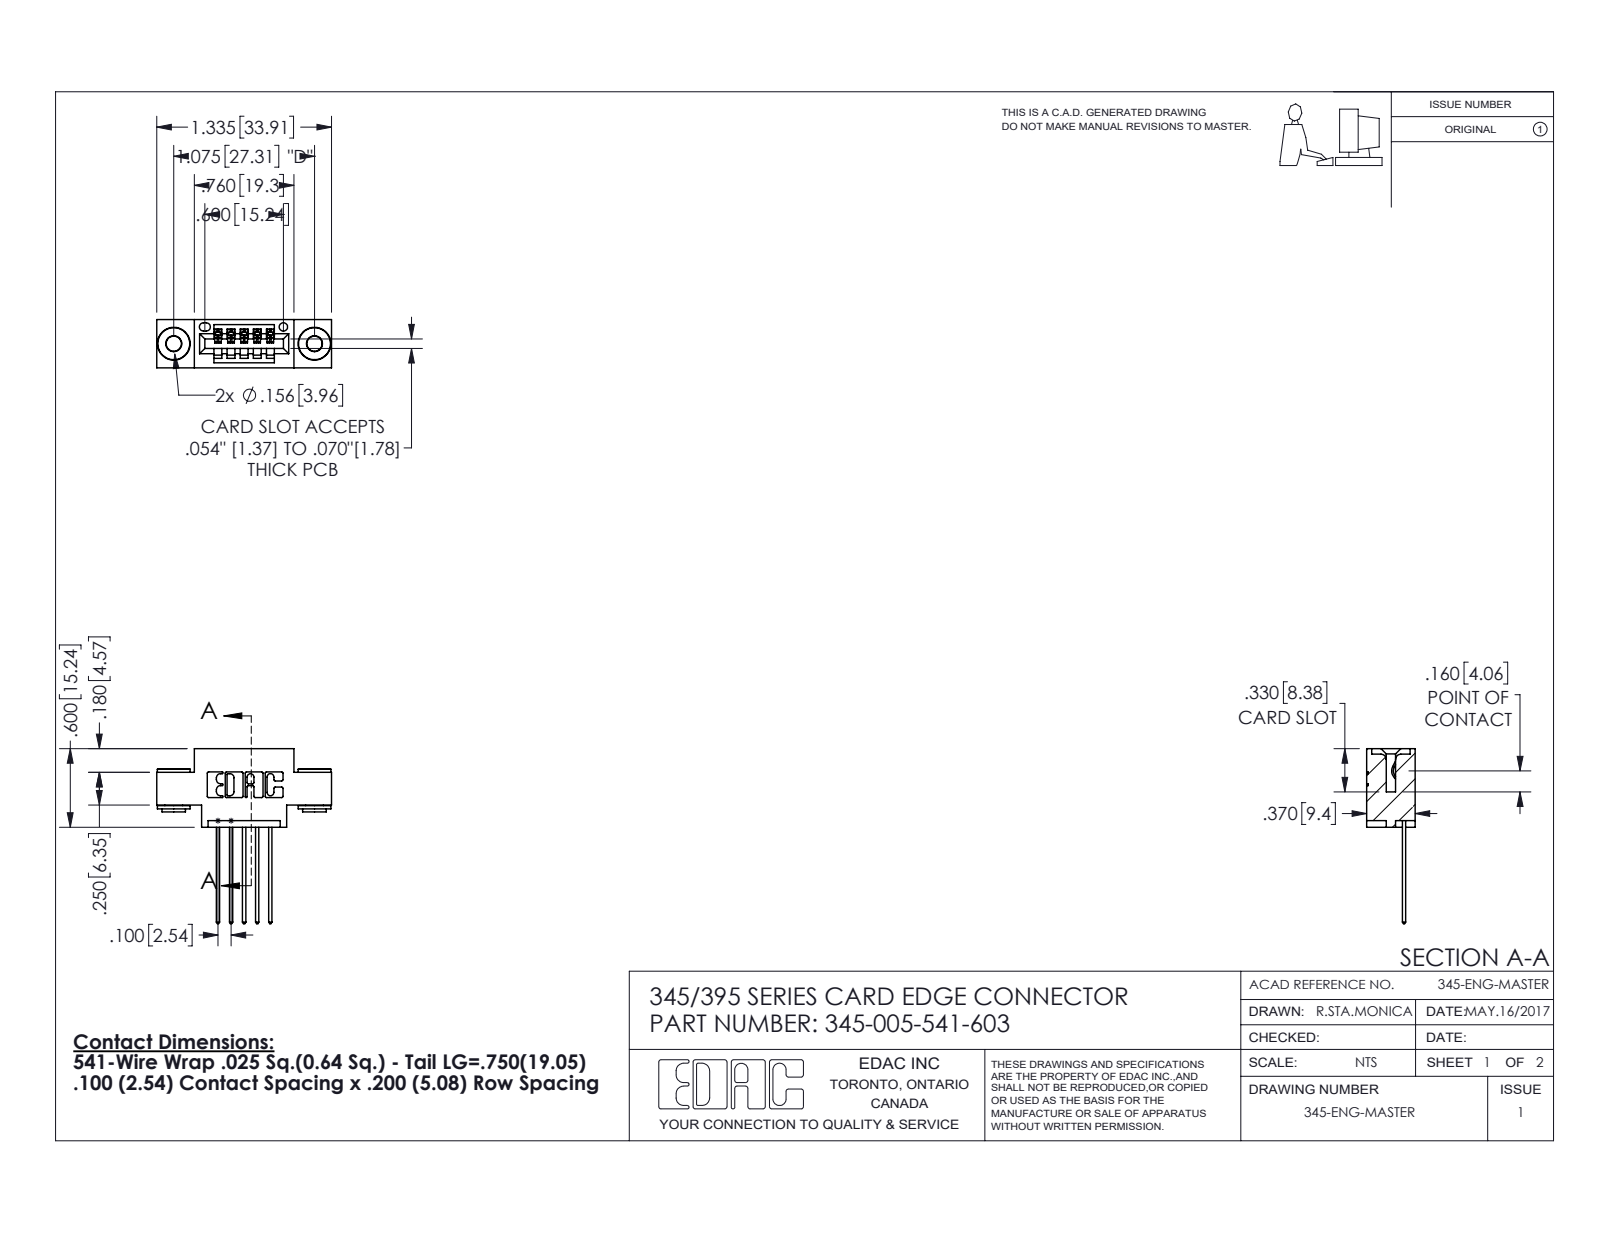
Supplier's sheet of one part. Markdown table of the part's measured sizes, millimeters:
| quantity | value |
| --- | --- |
| part name | 345-292-001_345-293-141; 345-250-002_345-250-002-102; 345-005-541-603; 345 Part_0.170 Offset - 0.156 Dia-TH |
| STEP written by | SolidWorks 2016 (CONFIG_CONTROL_DESIGN) |
| units | millimeters |
| bodies | 8 solids, 458 faces (294 planar, 156 cylindrical, 8 other) |
| overall size | 34 × 33.9 × 9.4 |
| volume | 2 830 mm³ |
| surface area | 3 710 mm² |
| round holes (diameter × count) | 2.9 × 2, 4 × 2, 1.6 × 1 |
| round bosses / shafts (diameter × count) | 6.4 × 2, 4.6 × 2, 3.5 × 2 |
| partial cylindrical surfaces (radius × count) | 0.3 × 22, 0.2 × 10, 0.3 × 10, 0.2 × 6, 0.8 × 6, 0.7 × 3, 0.8 × 2, 1 × 2 |
| main face-to-face distances | 9.4, 5.1, 1.8, 7.6, 2.5, 0.6, 2.5, 6.9, 6.4, 1.5 |
| hole center spacings | 6.9, 21.5, 27.3 |
